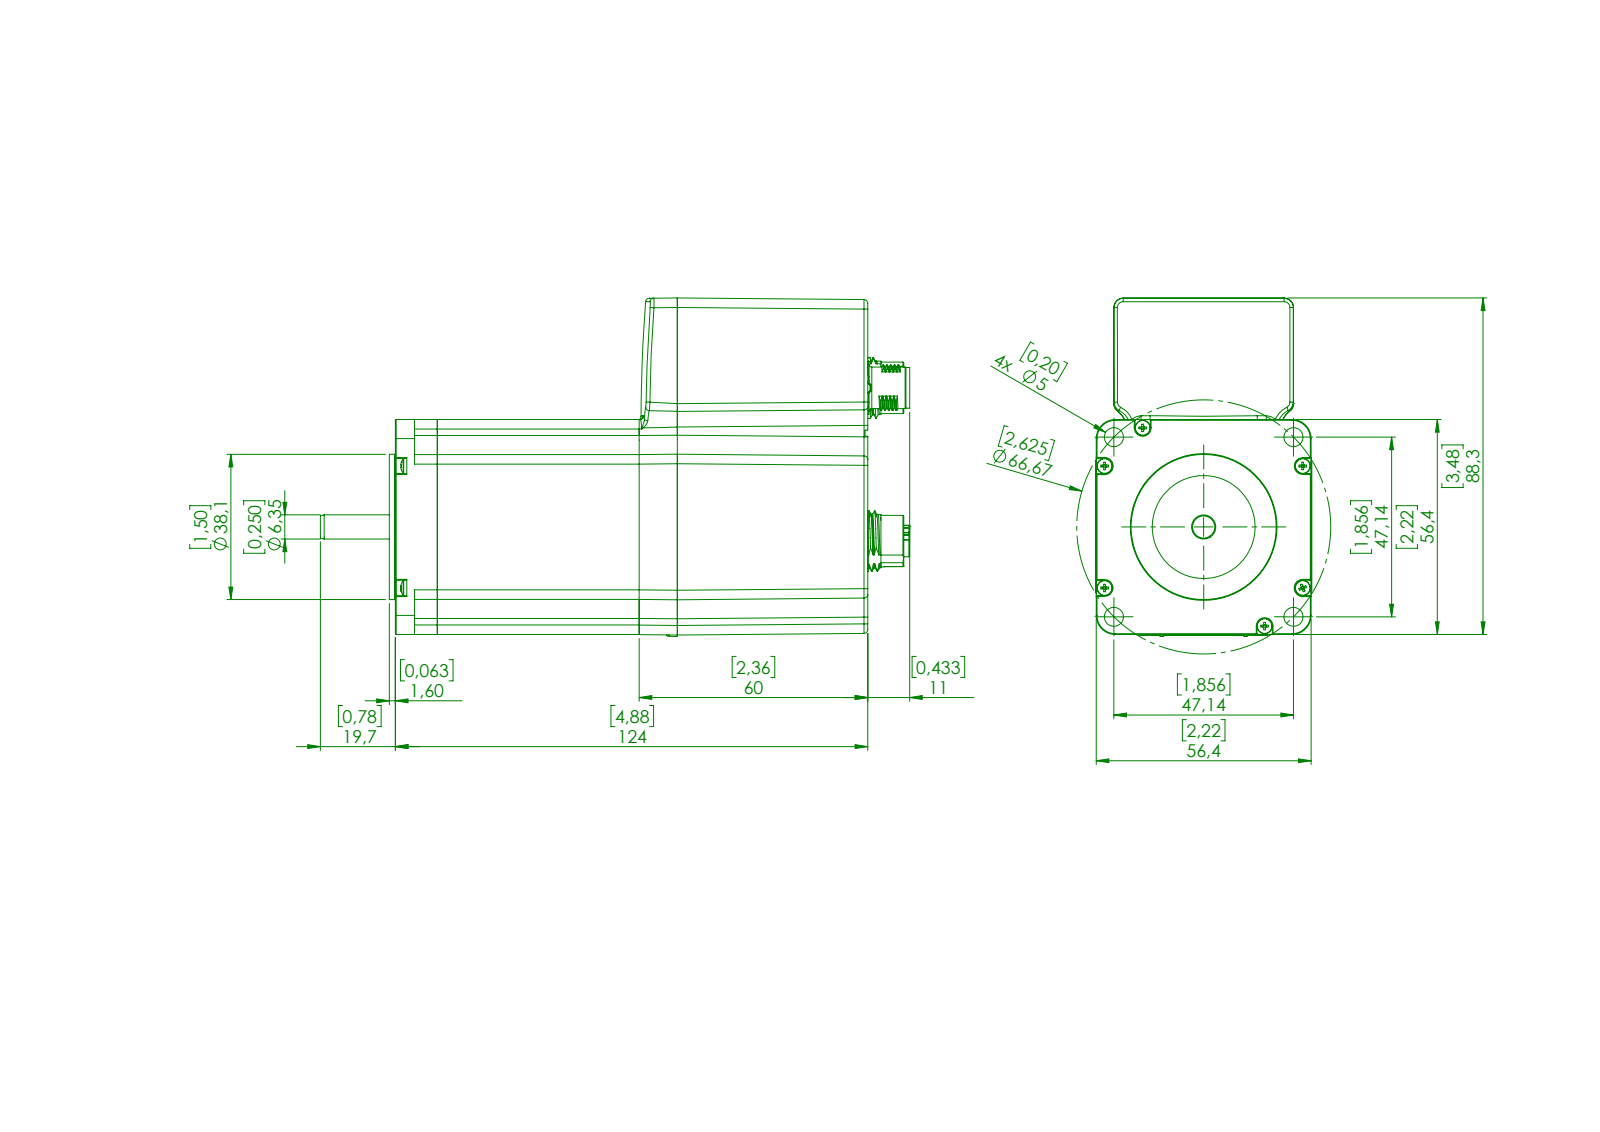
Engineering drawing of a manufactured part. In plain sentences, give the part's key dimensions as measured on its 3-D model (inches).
The part is named "Nema23 montado_F_ILong; Shaft SOLID; MM4100 V1_0 Rear Cover MIS23 G2 SOLID; Part4^MIS23X Solid (+8 more)". Its 3-D file was written by "SolidWorks 2017 (CONFIG_CONTROL_DESIGN)". It is 16 solids with 2517 faces: 874 planar, 734 cylindrical and 909 other. Overall it measures 6.091 by 3.497 by 2.231 inches. Its volume is 27.52 cubic inches and its surface area 112.1 square inches. Round holes: 27 of diameter 0.039, 6 of diameter 0.079, 6 of diameter 0.098, 4 of diameter 0.197, 3 of diameter 0.48, 2 of diameter 0.06, 2 of diameter 0.339, 2 of diameter 0.438, 2 of diameter 0.575, 1 of diameter 0.13, 1 of diameter 0.157, 1 of diameter 0.327. Round bosses or shafts: 17 of diameter 0.043, 17 of diameter 0.024, 13 of diameter 0.063, 7 of diameter 0.039, 5 of diameter 0.157, 4 of diameter 0.522, 3 of diameter 0.531, 3 of diameter 0.009. Partial cylindrical surfaces (rounded edges, fillets, slot ends): 64 of radius 0.008, 32 of radius 0.004, 29 of radius 0.098, 18 of radius 0.197, 16 of radius 0.039, 12 of radius 0.031, 10 of radius 0.006, 8 of radius 0.01. The main face-to-face distances are 0.394, 2.48, 2.087, 2.22, 1.941, 2.335, 4.421, 0.187, 0.433, 4.854. The hole center spacings are 0.098, 0.139, 1.561, 0.024, 0.306, 0.313, 1.181, 1.202.
